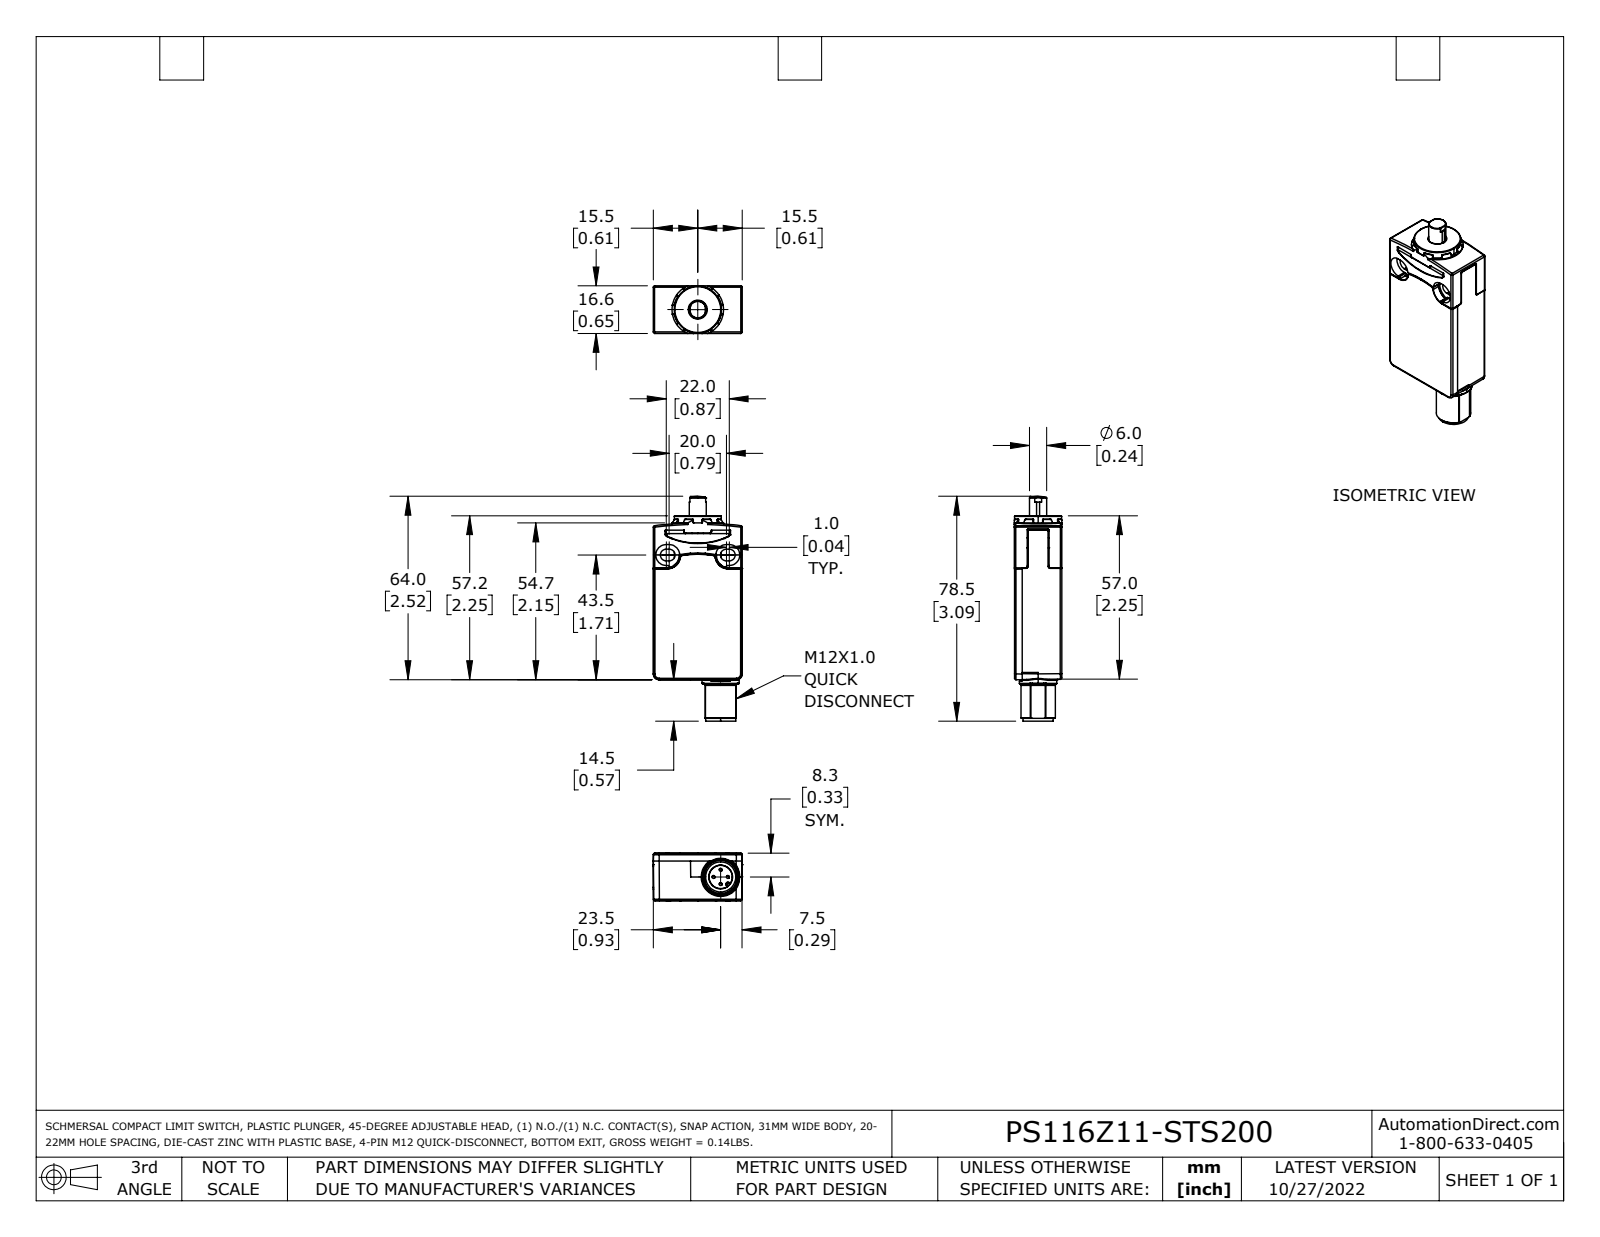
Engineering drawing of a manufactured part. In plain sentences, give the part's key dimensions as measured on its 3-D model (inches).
The part is named "PS116Z11-STS200_Default". Its 3-D file was written by "SolidWorks 2021 (CONFIG_CONTROL_DESIGN)". It is 1 solid with 873 faces: 266 planar, 382 cylindrical and 225 other. Overall it measures 3.091 by 1.22 by 0.654 inches. Its volume is 1.714 cubic inches and its surface area 16.68 square inches. Round holes: 2 of diameter 0.079, 1 of diameter 0.244, 1 of diameter 0.327, 1 of diameter 0.571. Round bosses or shafts: 4 of diameter 0.039, 2 of diameter 0.512, 1 of diameter 0.646, 1 of diameter 0.567, 1 of diameter 0.524, 1 of diameter 0.413, 1 of diameter 0.236. Partial cylindrical surfaces (rounded edges, fillets, slot ends): 110 of radius 0.008, 67 of radius 0.004, 34 of radius 0.02, 10 of radius 0.014, 8 of radius 0.039, 5 of radius 0.079, 4 of radius 0.081, 4 of radius 0.118. The main face-to-face distances are 0.65, 0.652, 1.22, 0.118, 0.654, 0.177, 0.535, 0.356, 0.116, 0.533. The hole center spacings are 0.315.
